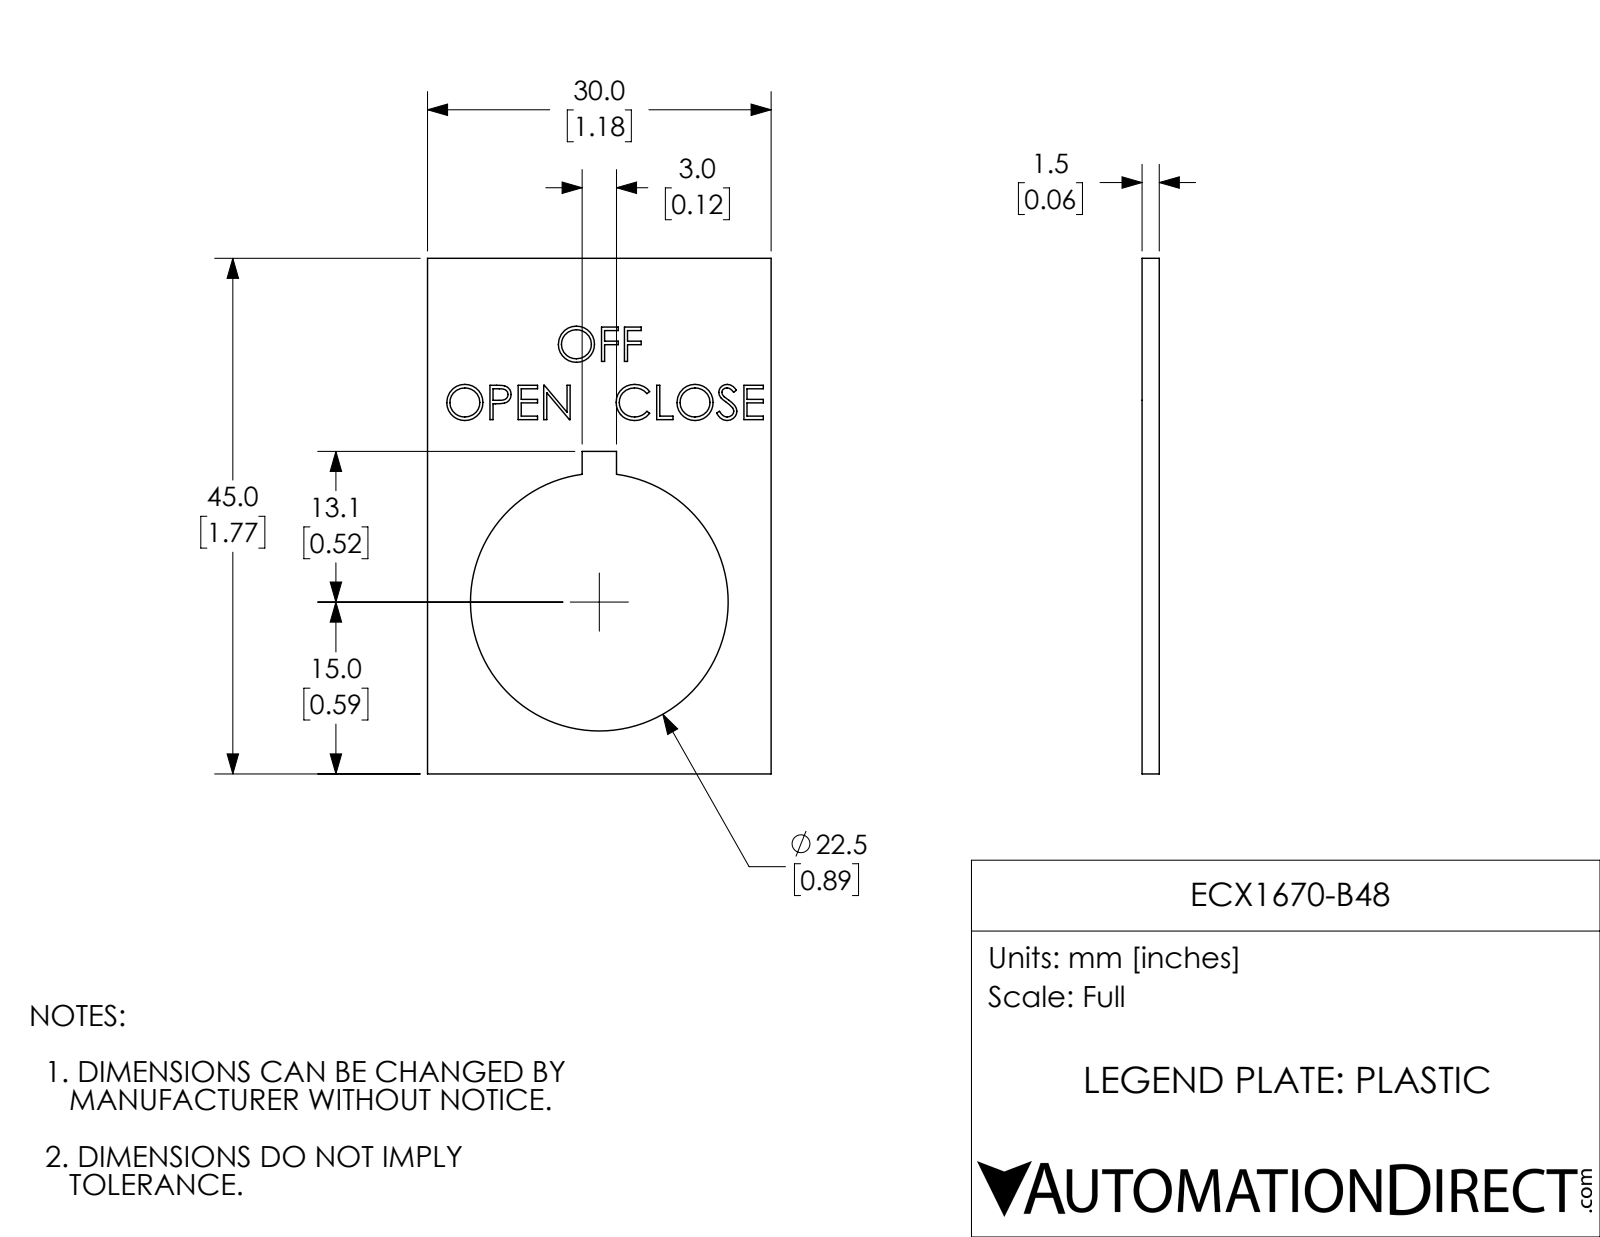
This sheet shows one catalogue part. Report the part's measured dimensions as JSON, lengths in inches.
{"part_name": "ECX1670-B48", "step_written_by": "SolidWorks 2017 (AUTOMOTIVE_DESIGN)", "units": "inches", "bodies": {"solids": 1, "faces": 154, "planar": 97, "cylindrical": 3, "other": 54}, "overall_size": [1.772, 1.181, 0.059], "volume_in3": 0.087, "surface_area_in2": 3.464, "round_holes": [[0.886, 1]], "face_to_face_distances": [0.059, 1.181, 1.772, 0.058, 0.531, 0.65, 1.108, 0.663, 0.118, 0.012]}
